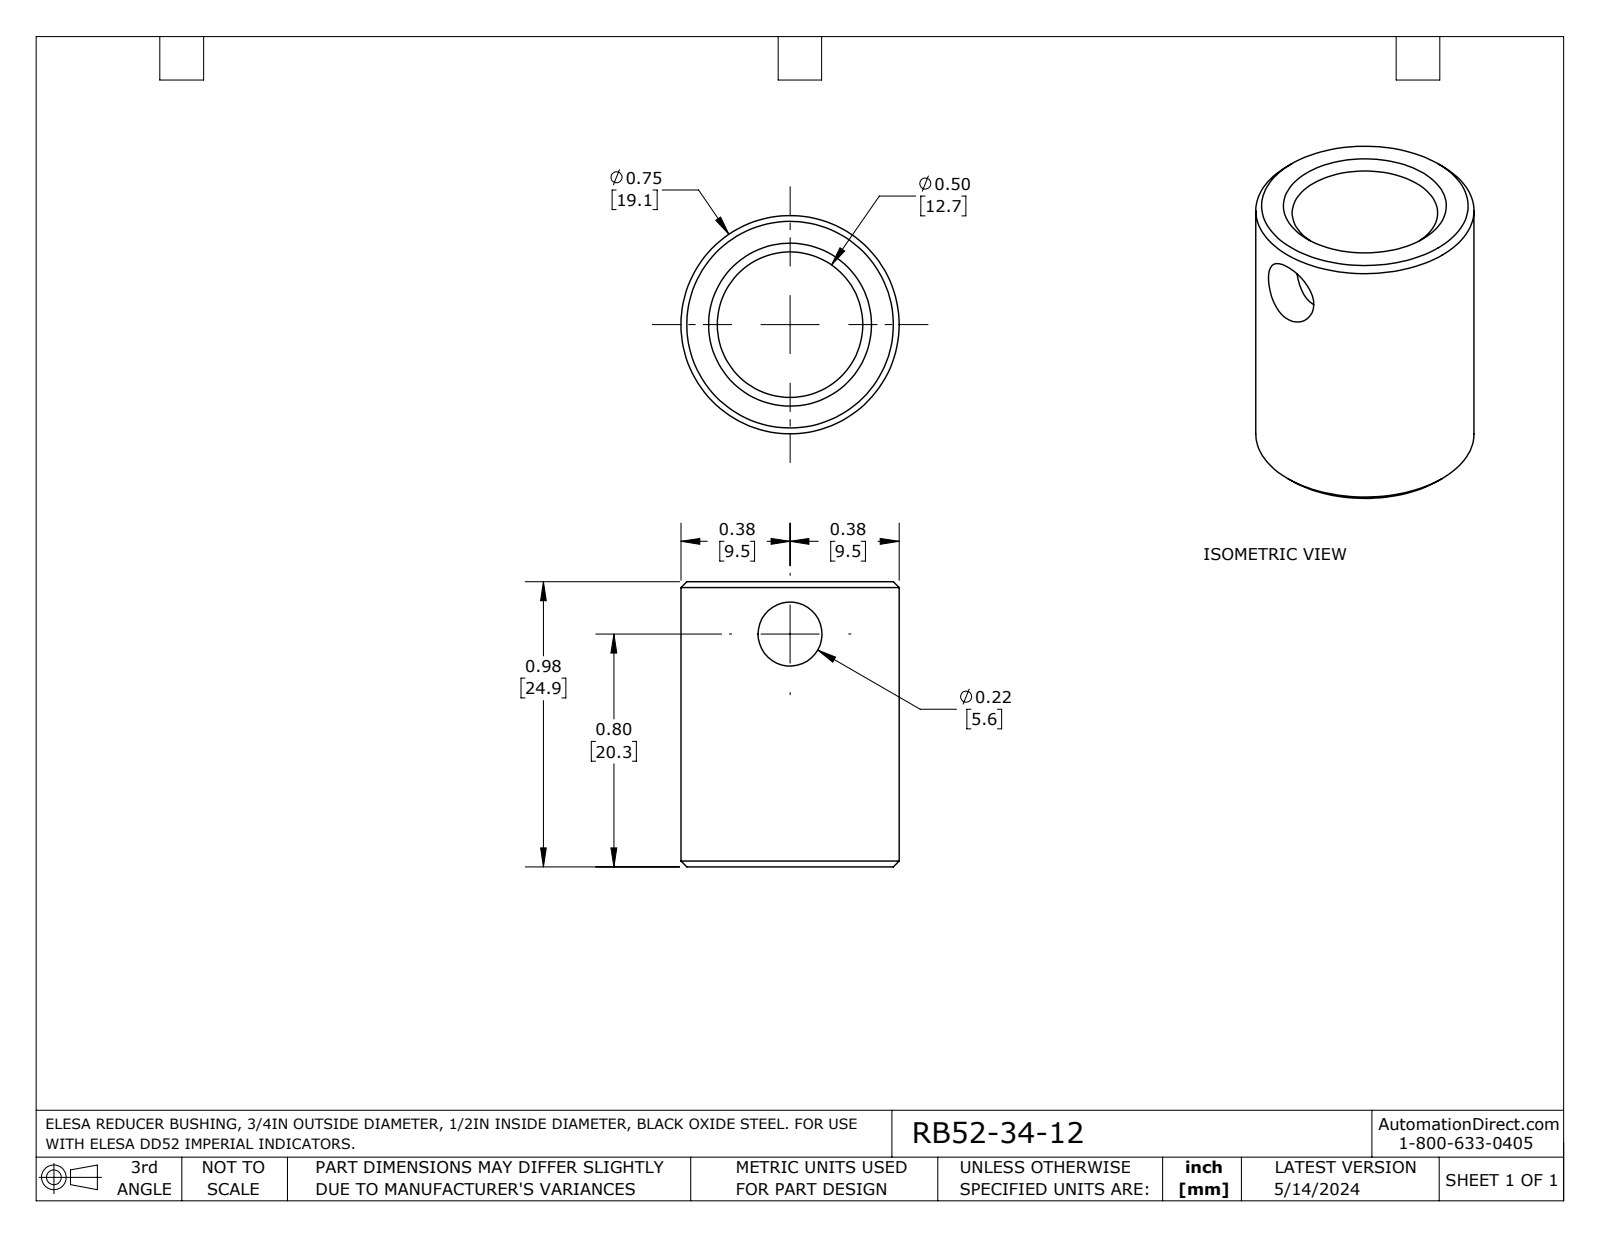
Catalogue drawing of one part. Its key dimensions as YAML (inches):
part_name: "RB52 3_4-1_2"
step_written_by: "SolidWorks 2023 (AUTOMOTIVE_DESIGN)"
units: inches
bodies: {solids: 1, faces: 9, planar: 2, cylindrical: 3, other: 4}
overall_size: [0.98, 0.75, 0.75]
volume: 0.233
surface_area: 4.242
round_holes:
  - {diameter: 0.22, count: 1}
  - {diameter: 0.5, count: 1}
round_bosses_or_shafts:
  - {diameter: 0.75, count: 1}
face_to_face_distances: [0.98]
